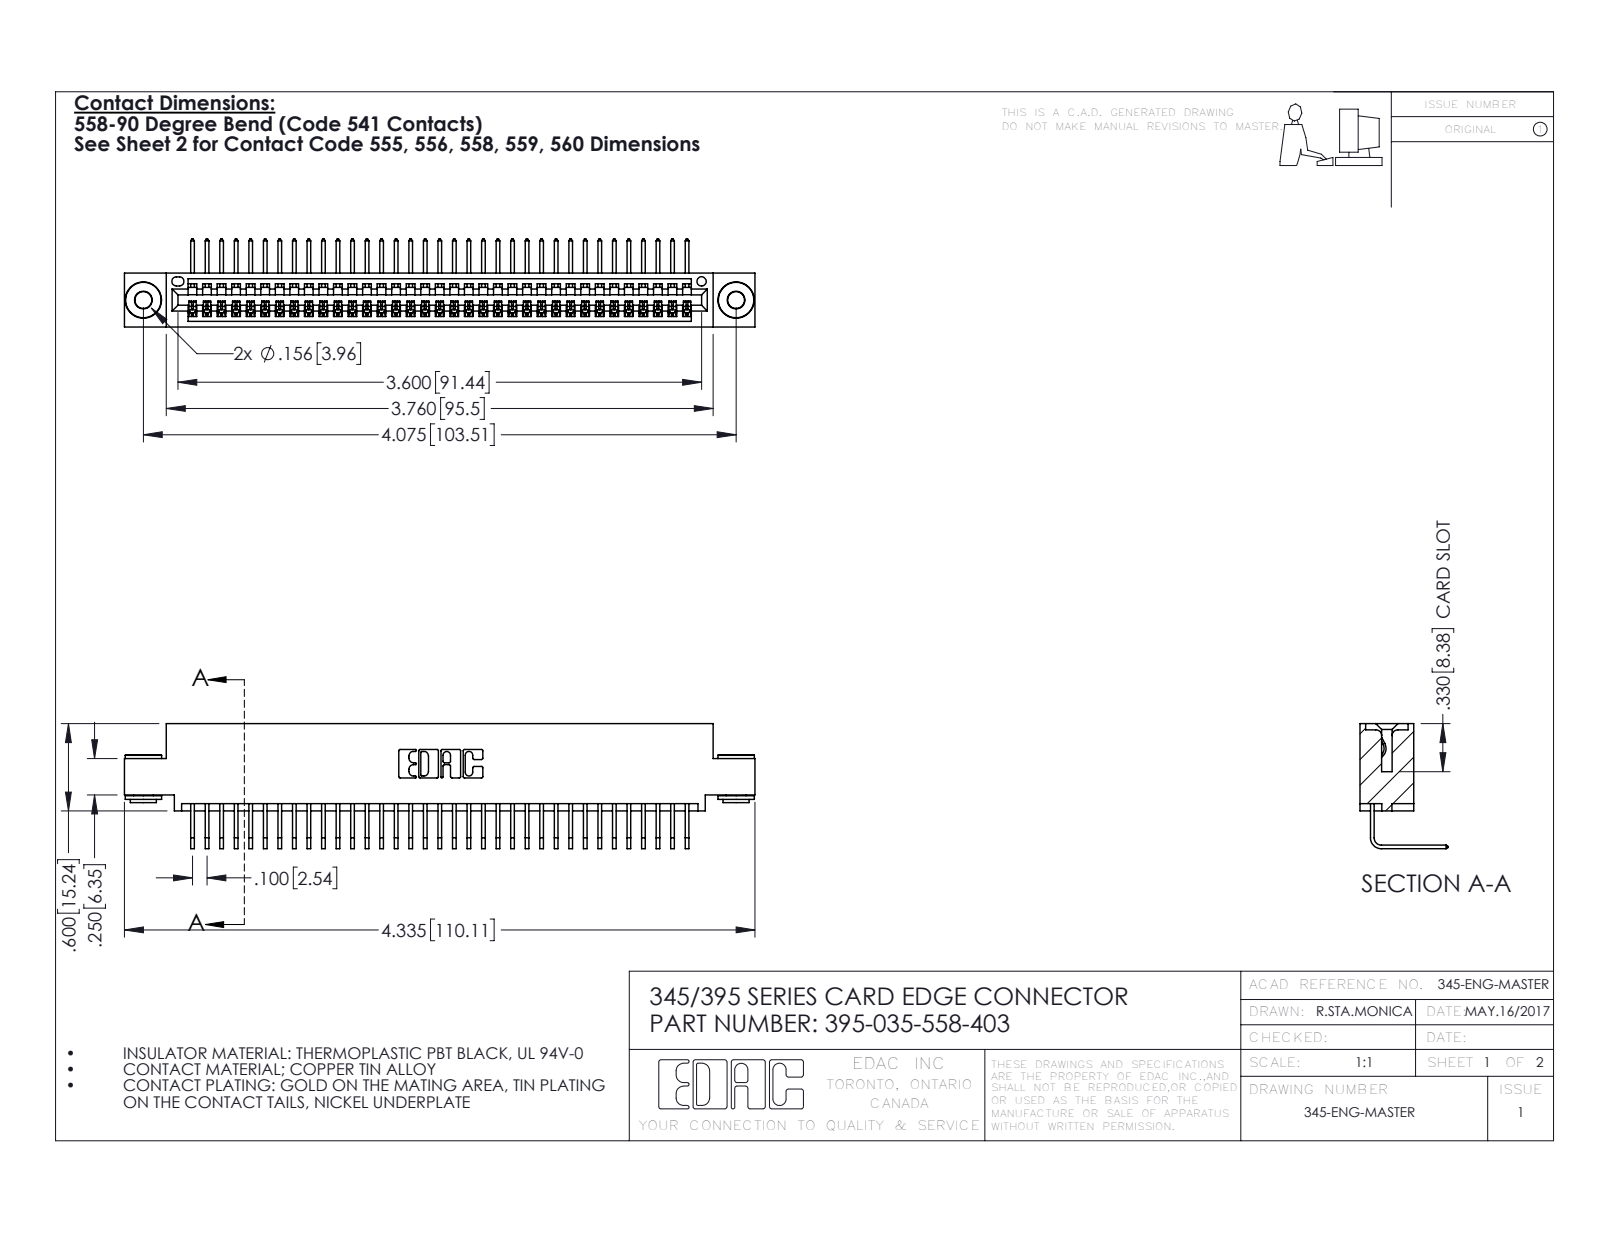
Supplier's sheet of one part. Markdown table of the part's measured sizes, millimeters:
| quantity | value |
| --- | --- |
| part name | 345 Part_0.110 Offset - 0.156 Dia-TH; 395-035-558-403; 345-292-001_558 Tail - 2; 345-250-002_345-250-002-102 |
| STEP written by | SolidWorks 2016 (CONFIG_CONTROL_DESIGN) |
| units | millimeters |
| bodies | 38 solids, 2268 faces (1564 planar, 696 cylindrical, 8 other) |
| overall size | 110.1 × 21.8 × 15.4 |
| volume | 10 500 mm³ |
| surface area | 14 790 mm² |
| round holes (diameter × count) | 2.9 × 2, 4 × 2, 1.6 × 1 |
| round bosses / shafts (diameter × count) | 6.4 × 2, 4.6 × 2, 3.5 × 2 |
| partial cylindrical surfaces (radius × count) | 0.2 × 70, 0.3 × 22, 0.2 × 6, 0.8 × 6, 0.7 × 3, 0.8 × 2, 1 × 2, 0.4 × 1 |
| main face-to-face distances | 1.8, 7.6, 9.4, 5.1, 0.6, 2.5, 6.9, 5.7, 3.8, 1.8 |
| hole center spacings | 6.9, 97.5, 103.5 |
